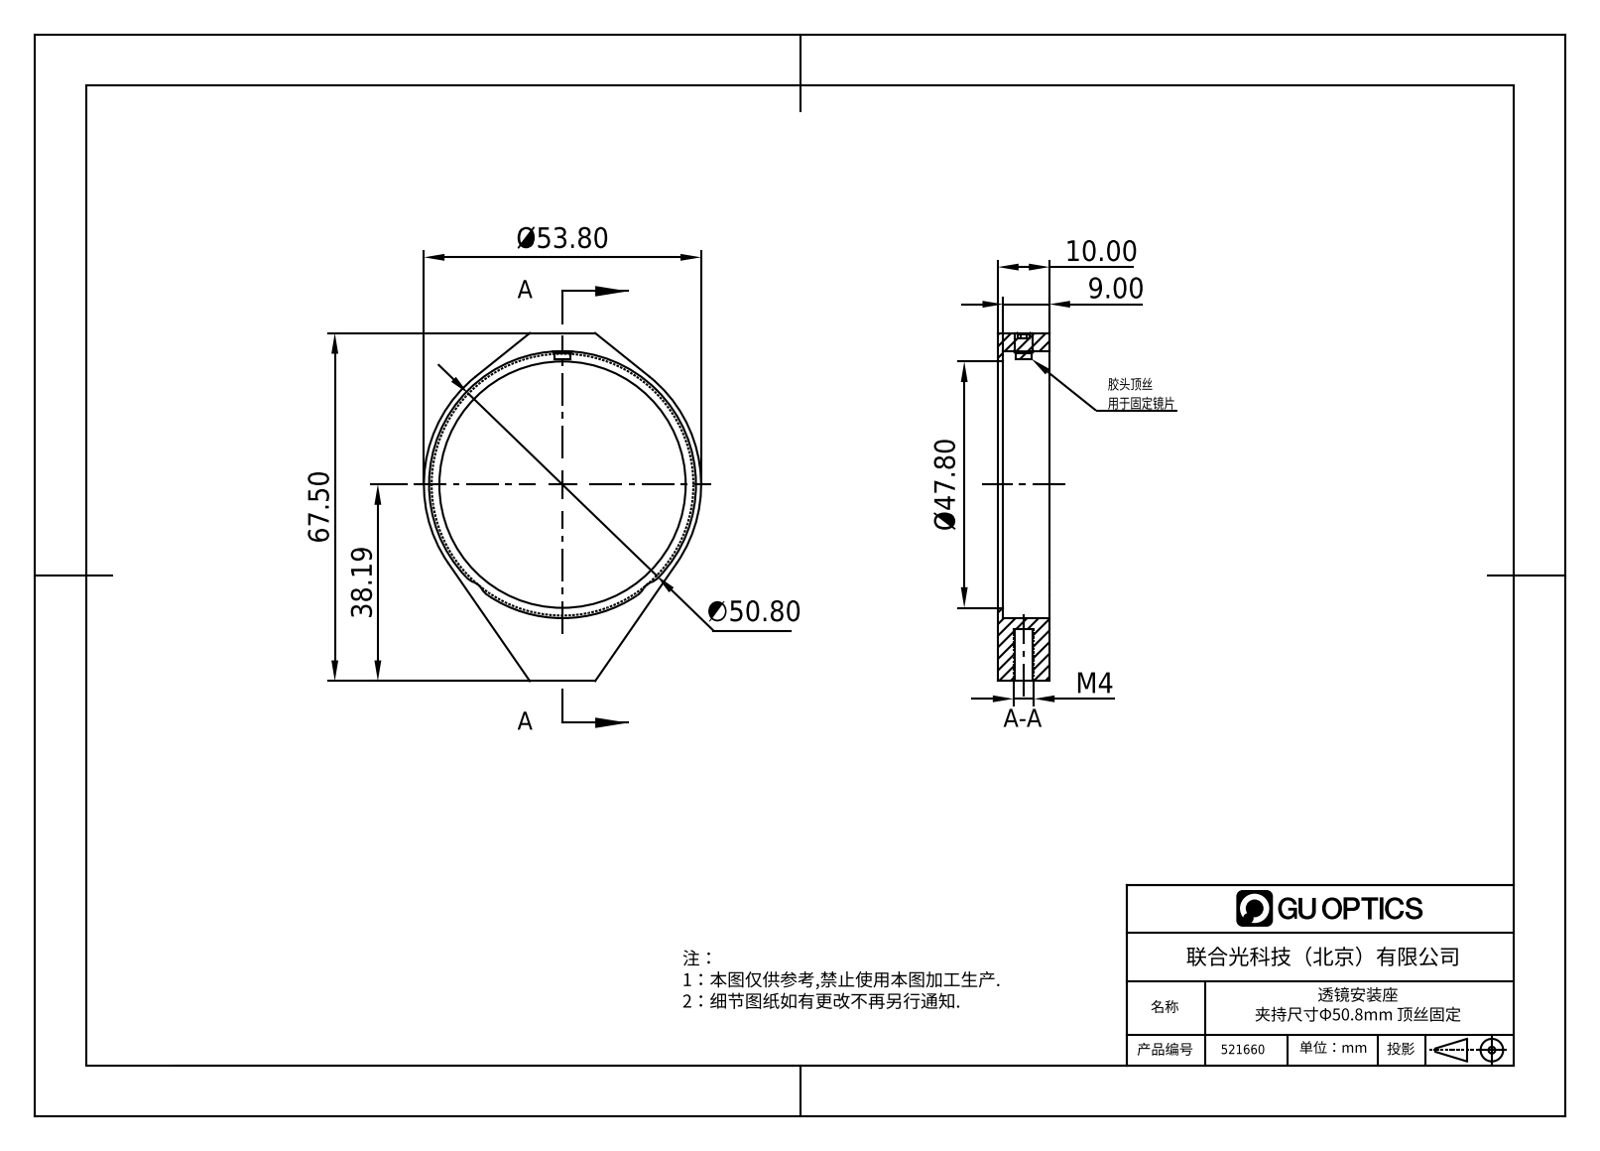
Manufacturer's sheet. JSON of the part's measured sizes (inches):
{"part_name": "1.3.1.20_ZZT-2.0-D", "step_written_by": "SolidWorks 2021 (CONFIG_CONTROL_DESIGN)", "units": "inches", "bodies": {"solids": 0, "faces": 45, "planar": 18, "cylindrical": 21, "other": 6}, "overall_size": [2.657, 2.118, 0.394], "round_holes": [[0.13, 1], [0.157, 1], [1.882, 1], [2.039, 1]], "round_bosses_or_shafts": [[0.118, 1]], "partial_cylinders_radius": [[0.157, 4], [0.118, 2], [1.059, 1]], "face_to_face_distances": [0.394, 0.039, 0.354, 2.657, 2.461, 0.197, 2.618, 0.157, 0.079]}
